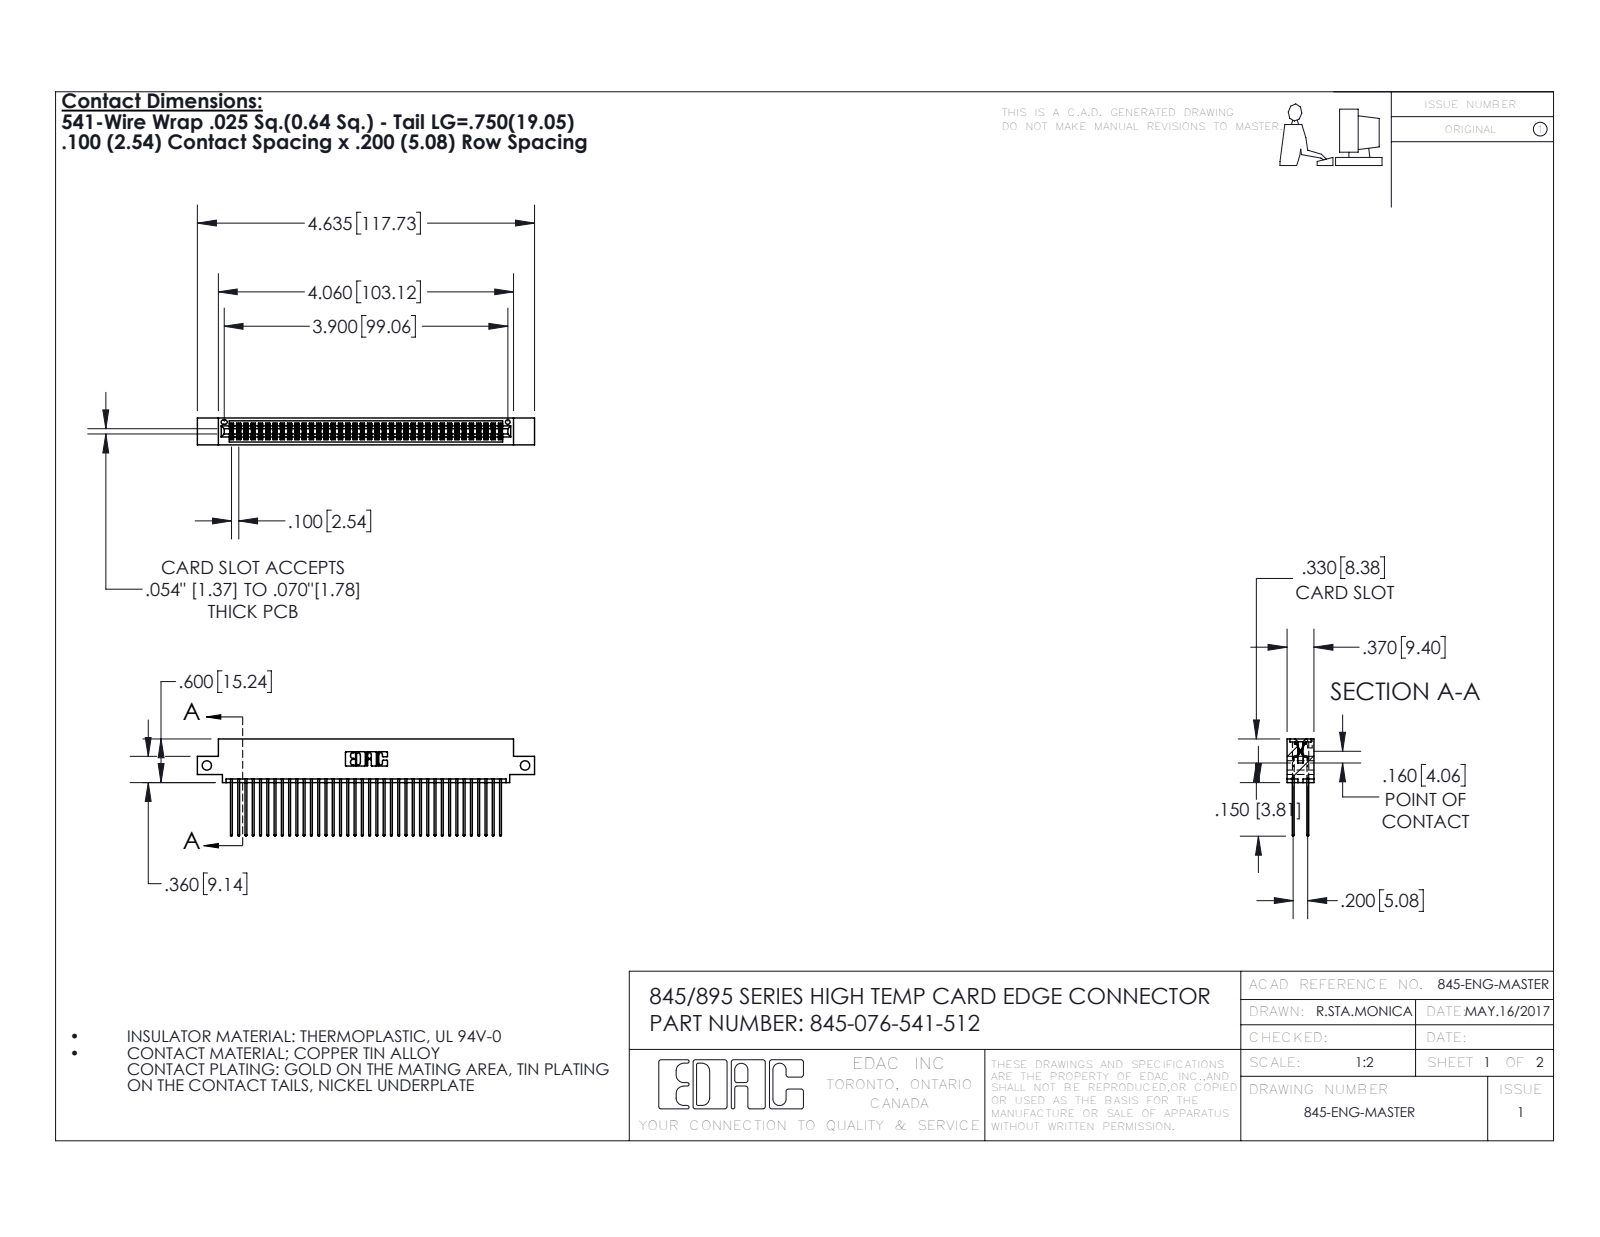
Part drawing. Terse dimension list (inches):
name: 345 Part_0.110 Offset - Side Mount; 345-076-541-512; 345-292-001_345-293-141
written by: SolidWorks 2016 (CONFIG_CONTROL_DESIGN)
unit: in
bodies: 77 solids, 3930 faces (2592 planar, 1338 cylindrical, 0 other)
size: 4.635 × 1.337 × 0.37
volume: 0.712 in³; area: 29.74 in²
holes: 2× ⌀0.128, 1× ⌀0.064
rounds: 115× R0.006, 76× R0.01, 22× R0.01, 6× R0.007, 6× R0.031, 3× R0.026, 2× R0.014, 2× R0.019
face distances: 0.298, 0.072, 0.2, 0.098, 0.272, 0.025, 0.225, 0.37, 0.175, 0.149
hole spacings: 4.375
